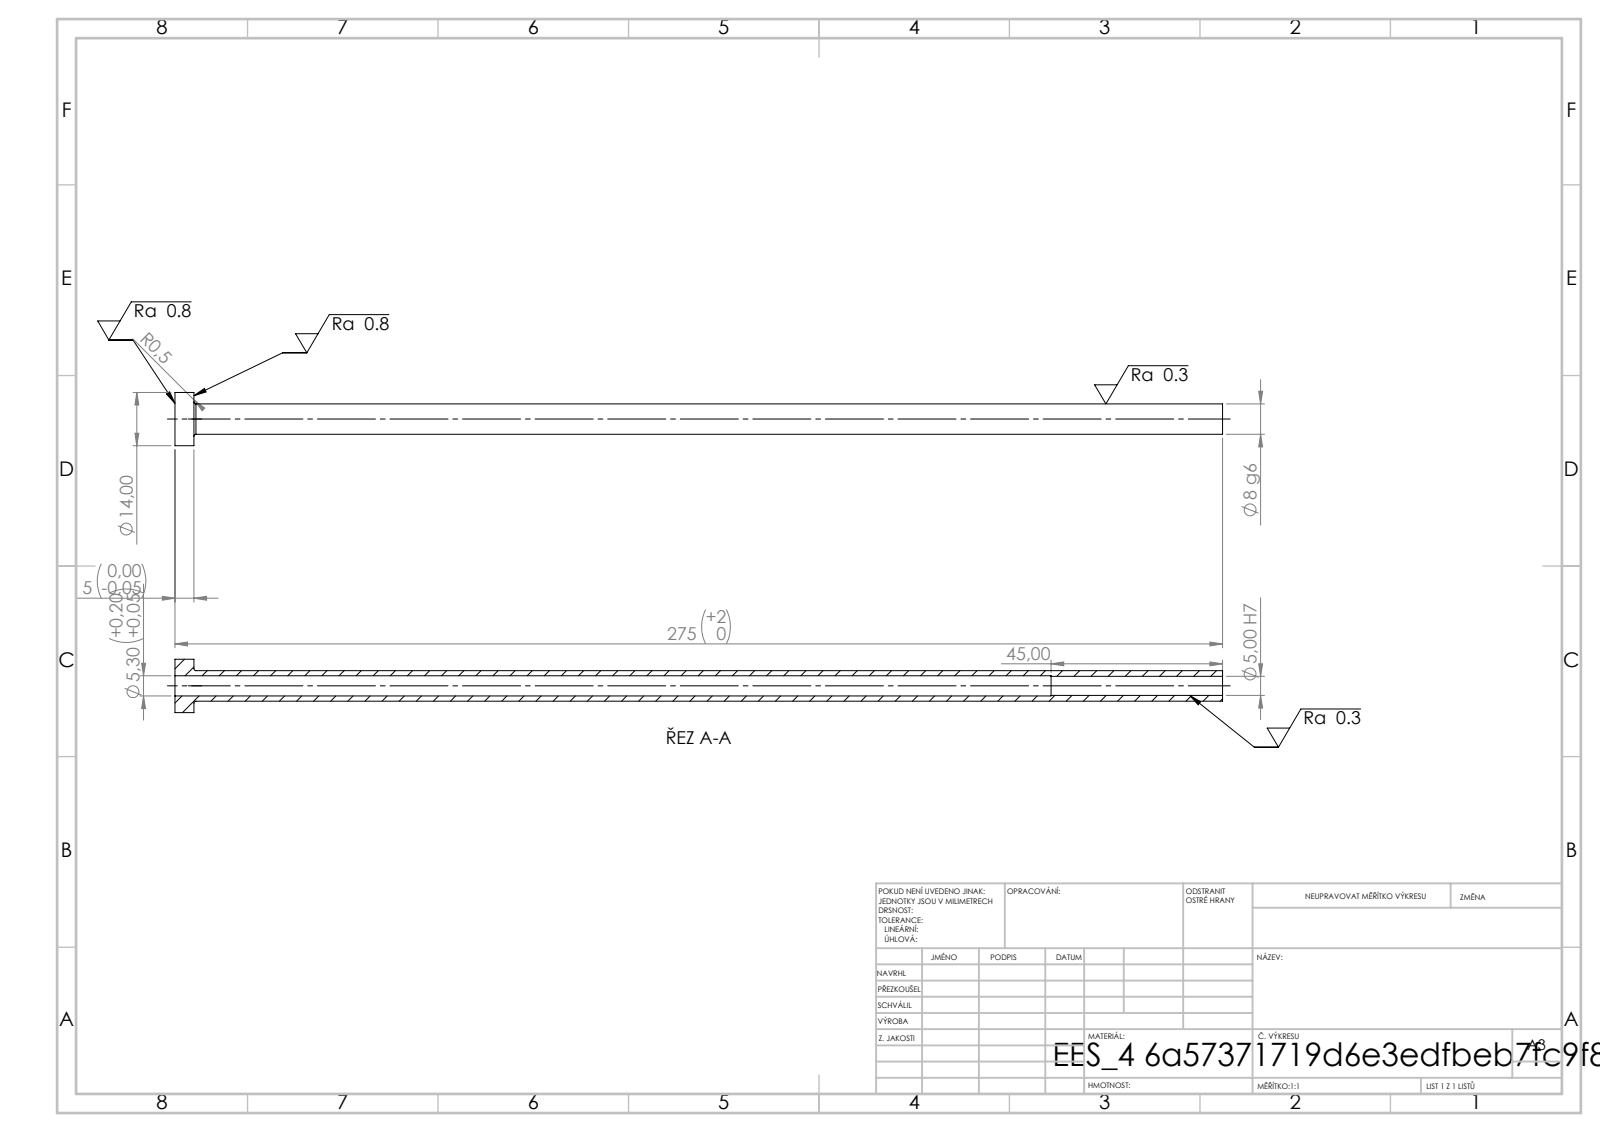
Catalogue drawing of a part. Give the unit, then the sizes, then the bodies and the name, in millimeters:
Units: millimetres
Overall size (bounding box): 275 × 14 × 14
Round holes (diameter × count): ⌀5 ×1, ⌀5.3 ×1
Round bosses / shafts (diameter × count): ⌀14 ×1, ⌀8 ×1
Main face-to-face distances: 5, 275, 270, 230, 225, 45
Volume: 8 385 mm³ · Surface area: 11 806 mm²
Bodies: 1 solid, 14 faces (4 planar, 8 cylindrical, 2 other)
STEP written by: SolidWorks 2019 (CONFIG_CONTROL_DESIGN)
